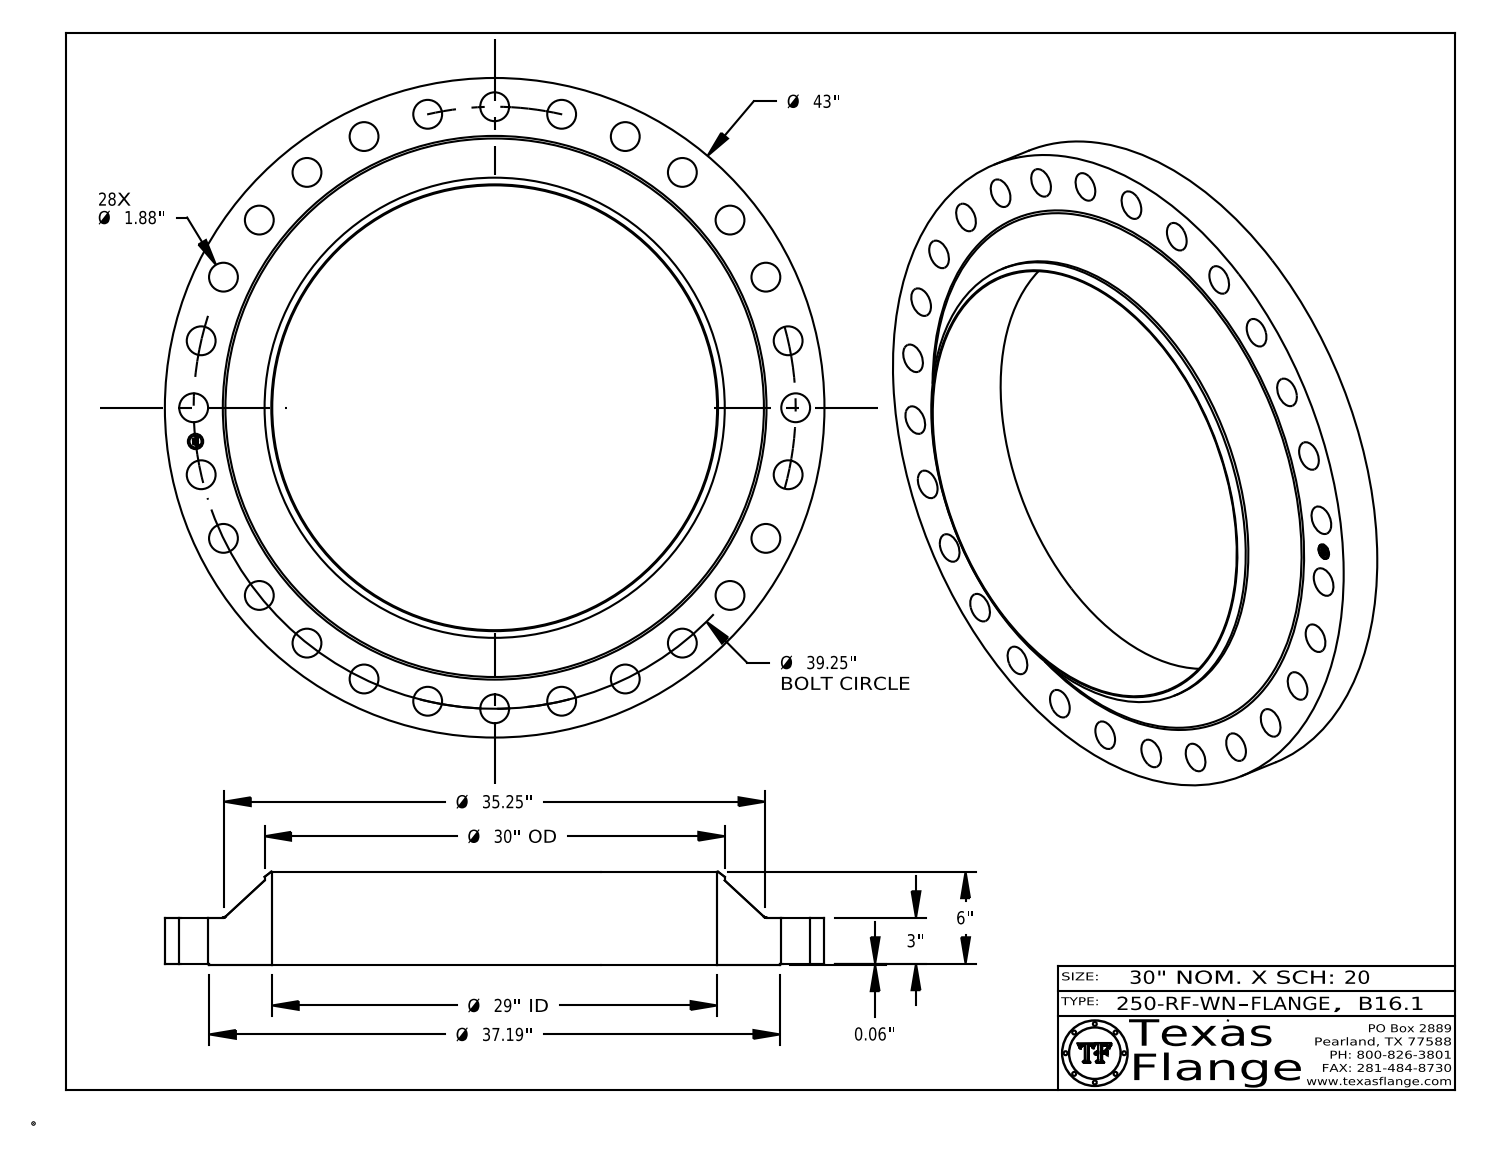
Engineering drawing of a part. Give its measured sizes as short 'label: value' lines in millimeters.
name: 250-RF-WN, B16.1
written by: CATIA V5 STEP AP203 (CONFIG_CONTROL_DESIGN)
unit: mm
bodies: 1 solid, 459 faces (369 planar, 84 cylindrical, 6 other)
size: 1092.2 × 1092.2 × 153.99
volume: 42 910 000 mm³; area: 1 947 000 mm²
holes: 28× ⌀47.75, 1× ⌀25.4, 1× ⌀736.6
bosses: 8× ⌀1.54, 1× ⌀1092.2, 1× ⌀944.63, 1× ⌀762, 1× ⌀20.01
face distances: 77.79, 76.2, 1.59, 153.99, 152.4, 77.41, 75.82, 0.38, 76.58, 7.58
hole spacings: 111.62, 221.84, 329.27, 432.56, 530.41, 898.22, 621.59, 844.14
